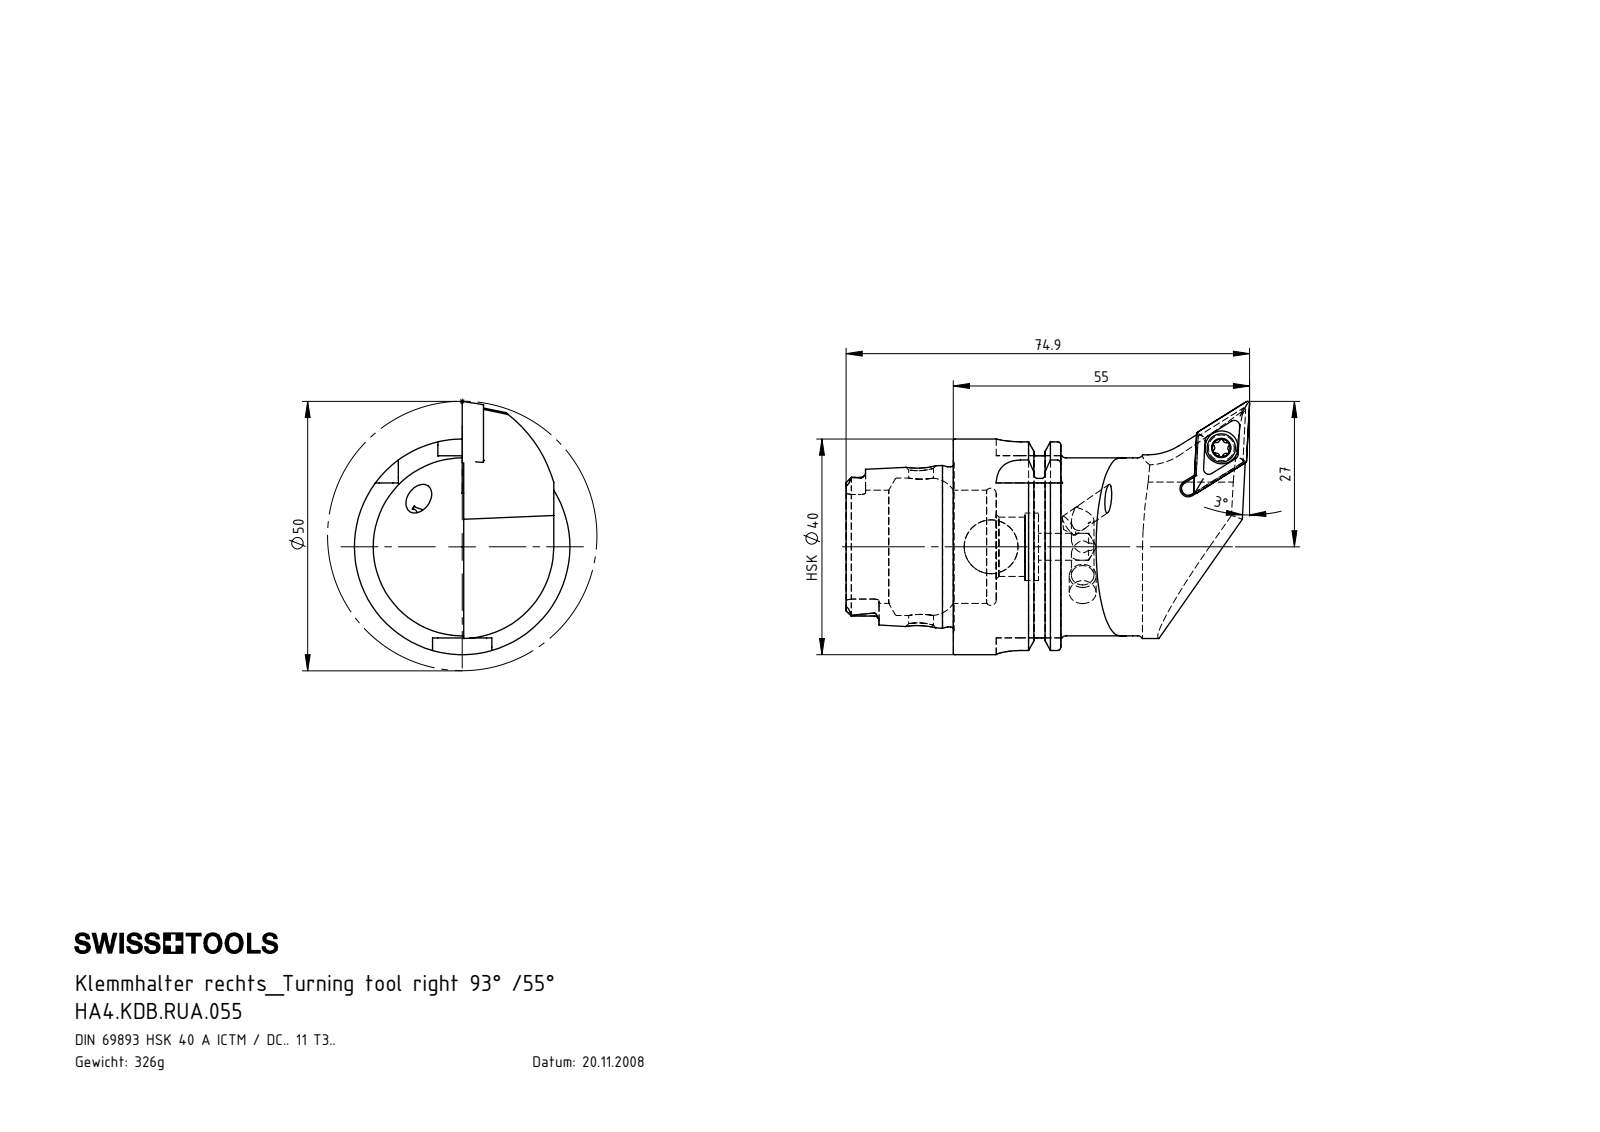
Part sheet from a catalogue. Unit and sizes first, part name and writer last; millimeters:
Units: millimetres
Overall size (bounding box): 74.9 × 47.01 × 40
Round holes (diameter × count): ⌀4.2 ×2, ⌀5 ×2, ⌀3.3 ×1, ⌀4 ×1, ⌀4.4 ×1, ⌀4.6 ×1, ⌀6.1 ×1, ⌀10 ×1, ⌀11 ×1, ⌀12.5 ×1, ⌀21 ×1, ⌀25.5 ×1
Round bosses / shafts (diameter × count): ⌀40 ×1, ⌀34.75 ×1, ⌀33 ×1, ⌀29.71 ×1, ⌀5.25 ×1, ⌀5 ×1, ⌀4 ×1
Partial cylindrical surfaces — rounded edges, fillets, slot ends (radius × count): R0.34 ×6, R0.59 ×6, R0.9 ×6, R4.5 ×4, R1.82 ×2, R1.88 ×2, R1.25 ×1, R3 ×1
Main face-to-face distances: 7.95, 16.7, 19.95, 12, 13.03, 3.67, 19.9, 27.85, 39.85, 35.7
Hole centre spacings: 46.51, 46.61
Volume: 41 293 mm³ · Surface area: 13 804 mm²
Bodies: 5 solids, 312 faces (80 planar, 91 cylindrical, 141 other)
Part name (STEP PRODUCT): DCMT11T304; HA4.KDB.RUA.055; KVT_MB_600_050; WCB-ER2.001.009_A (+1 more)
STEP written by: SolidWorks 2017 (AUTOMOTIVE_DESIGN)
